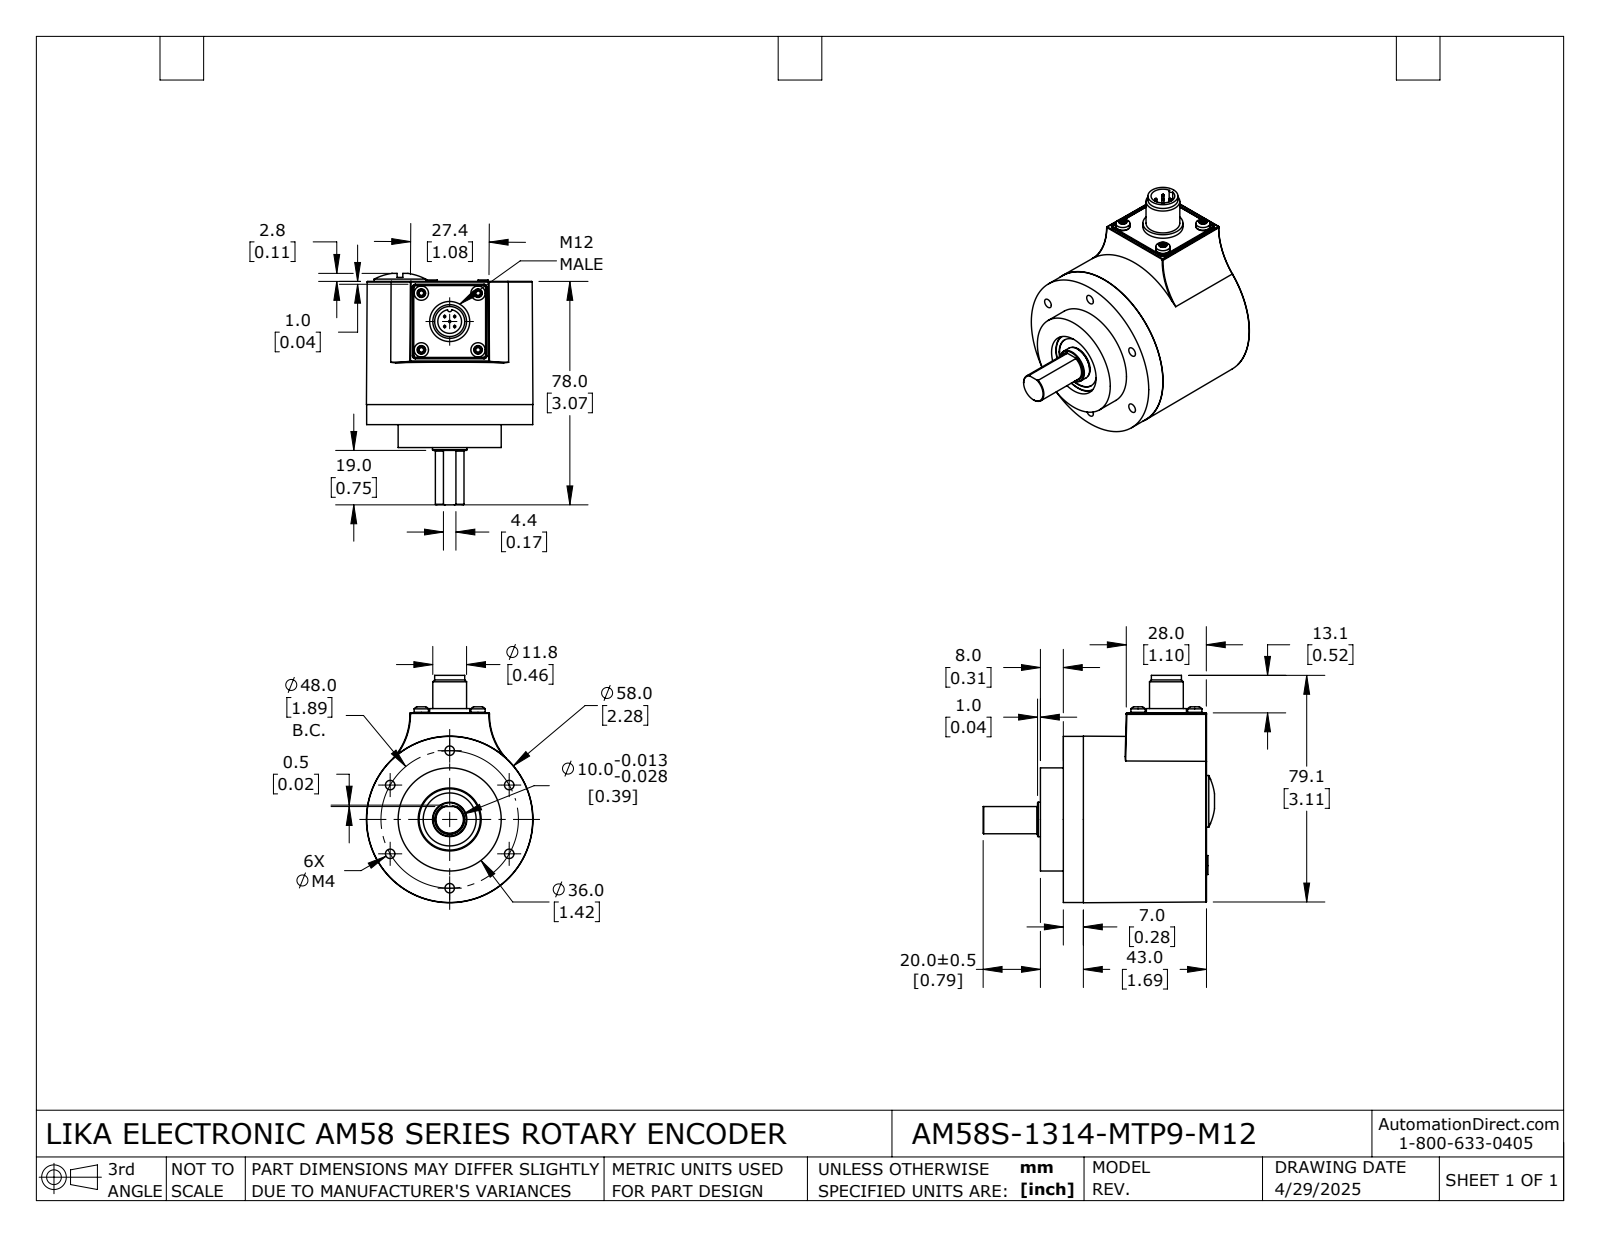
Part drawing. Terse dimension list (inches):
name: AM58S-1314-MTP9-M12
written by: SolidWorks 2024 (AUTOMOTIVE_DESIGN)
unit: in
bodies: 40 solids, 1396 faces (371 planar, 483 cylindrical, 542 other)
size: 3.406 × 2.283 × 2.283
volume: 3.742 in³; area: 76.06 in²
holes: 11× ⌀0.079, 10× ⌀0.047, 6× ⌀0.13, 5× ⌀0.081, 5× ⌀0.138, 4× ⌀0.063, 4× ⌀0.098, 3× ⌀0.492, 2× ⌀0.382, 2× ⌀0.429, 1× ⌀0.041, 1× ⌀0.126
bosses: 12× ⌀0.063, 12× ⌀0.039, 6× ⌀0.118, 3× ⌀0.524, 2× ⌀0.472, 1× ⌀2.283, 1× ⌀2.185, 1× ⌀2.165
rounds: 26× R0.008, 25× R0.039, 3× R0.118, 3× R0.269, 3× R0.299, 3× R0.317, 3× R0.354, 3× R0.392
face distances: 0.098, 0.394, 1.594, 0.079, 1.693, 0.276, 0.197, 0.039, 0.118, 0.315
hole spacings: 0.098, 0.139, 1.334, 0.197, 0.209, 0.295, 0.669, 0.791
